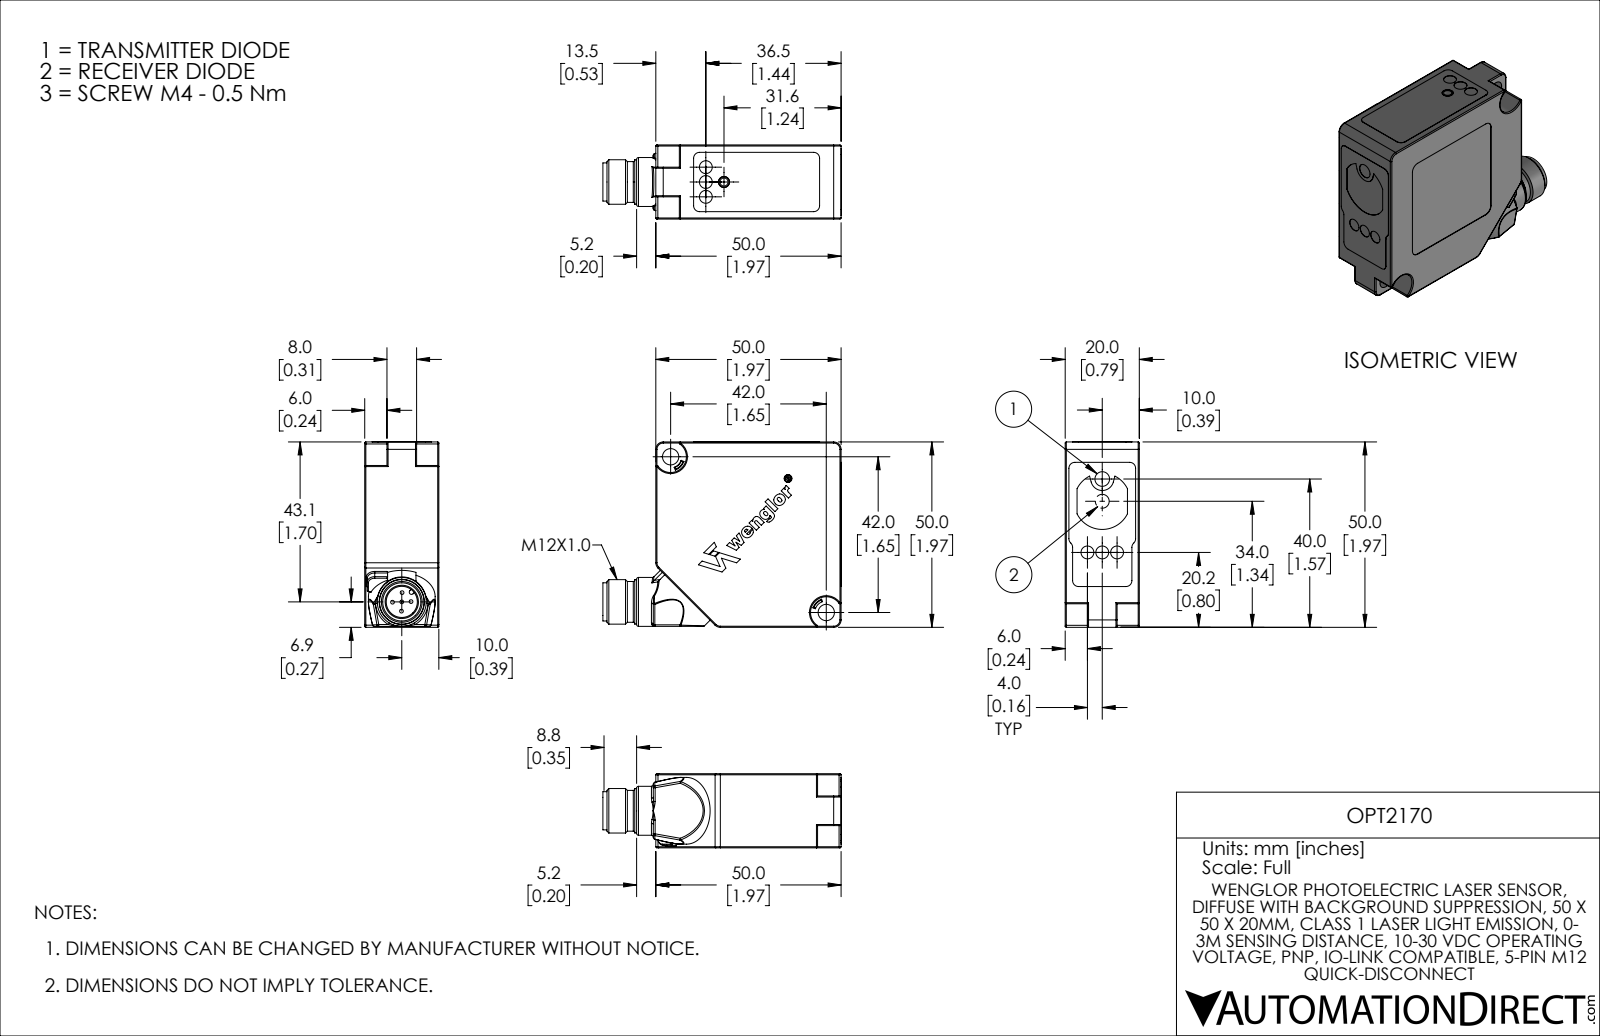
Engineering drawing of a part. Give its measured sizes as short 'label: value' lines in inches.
name: OPT2171
written by: SolidWorks 2021 (AUTOMOTIVE_DESIGN)
unit: in
bodies: 1 solid, 364 faces (79 planar, 172 cylindrical, 113 other)
size: 2.531 × 1.969 × 0.787
volume: 2.963 in³; area: 16.46 in²
holes: 3× ⌀0.137, 3× ⌀0.137, 2× ⌀0.173, 1× ⌀0.118, 1× ⌀0.156, 1× ⌀0.331, 1× ⌀0.394
bosses: 5× ⌀0.039, 1× ⌀0.709, 1× ⌀0.52, 1× ⌀0.472, 1× ⌀0.433, 1× ⌀0.406, 1× ⌀0.37, 1× ⌀0.055
rounds: 28× R0.012, 12× R0.063, 10× R0.079, 8× R0.008, 5× R0.02, 5× R0.037, 3× R0.122, 2× R0.035
face distances: 0.787, 0.783, 1.969, 1.969, 1.958, 1.959, 0.236, 0.551, 0.315, 0.232
hole spacings: 0.157, 0.249, 0.315, 0.548, 0.795, 0.193, 0.525, 0.78
